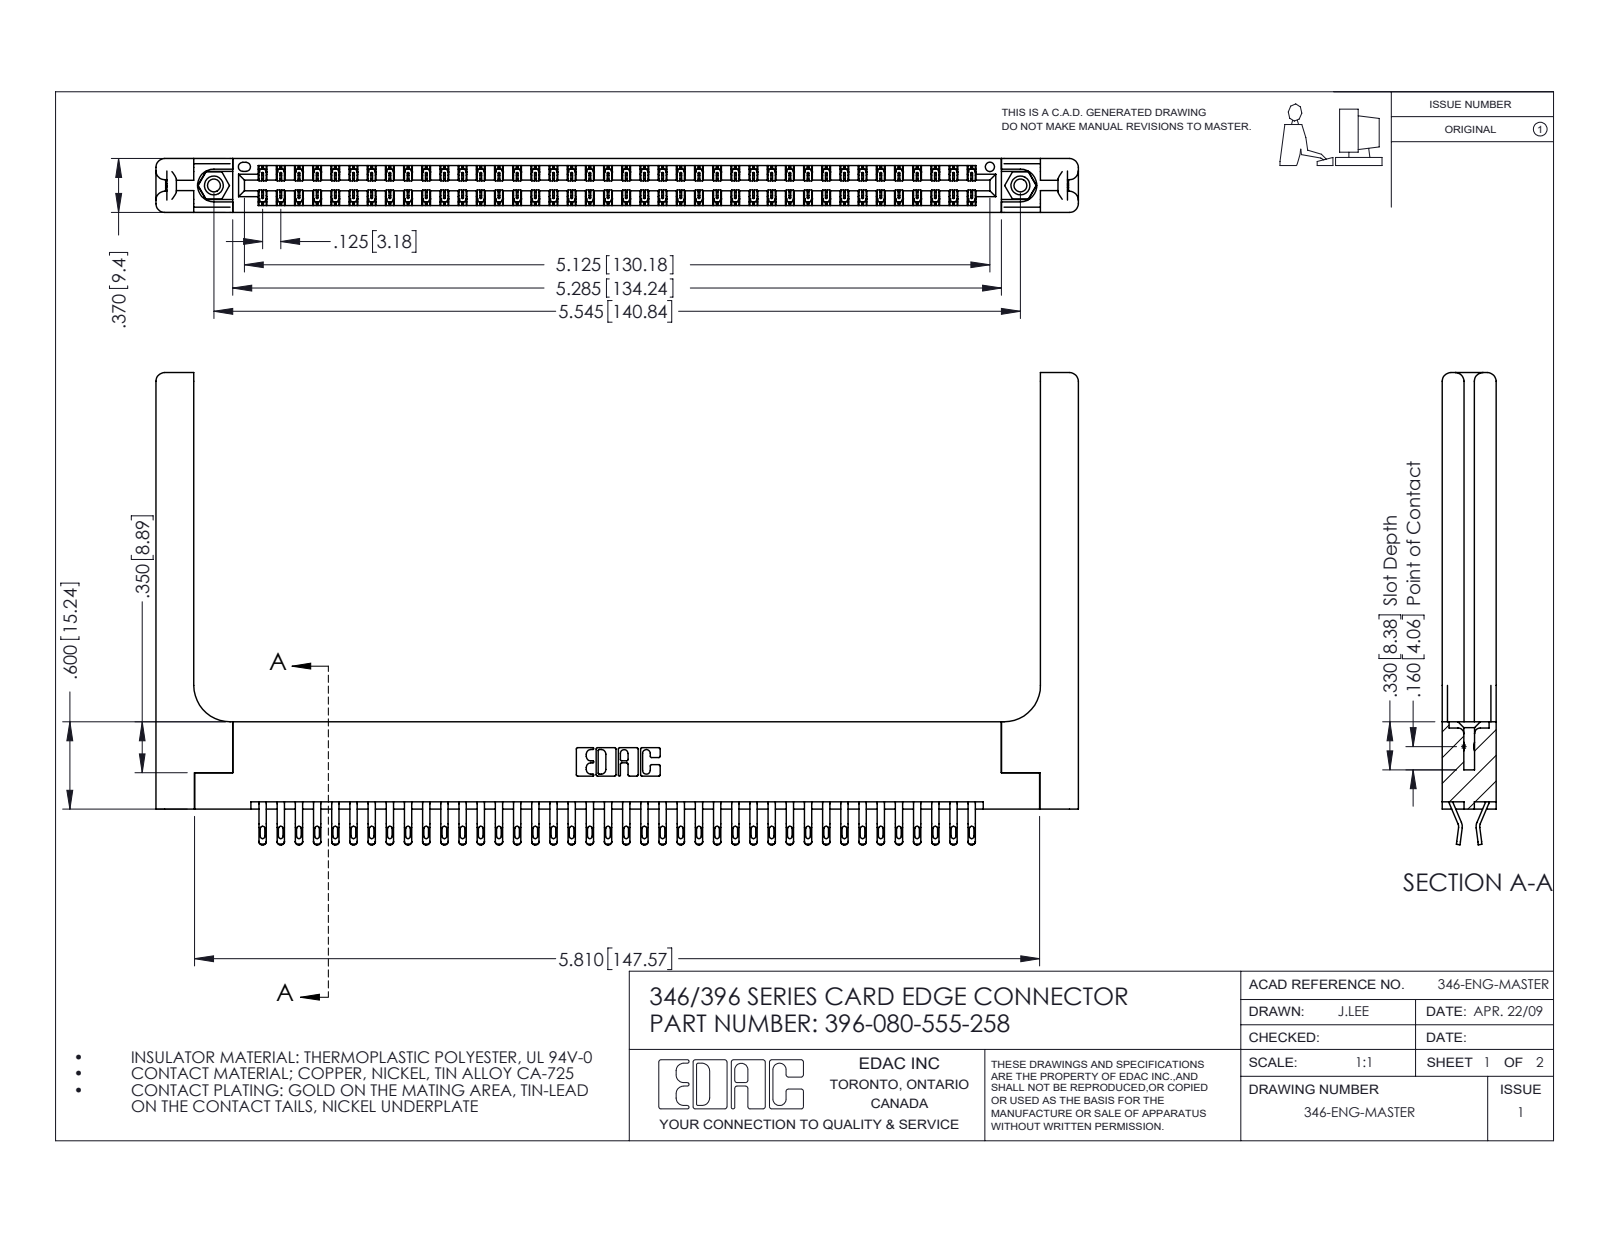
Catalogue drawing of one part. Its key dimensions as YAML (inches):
part_name: "345-250-001_345-250-001-102; 346-220-058_345-220-058; 346 Part_Flush Mounting Lugs - 0.156 Dia-TH; 345-292-001_555 Tail (+1 more)"
step_written_by: "SolidWorks 2016 (CONFIG_CONTROL_DESIGN)"
units: inches
bodies: {solids: 85, faces: 5018, planar: 2864, cylindrical: 2094, other: 60}
overall_size: [6.341, 3.245, 0.37]
volume: 1.429
surface_area: 42.86
round_holes:
  - {diameter: 0.089, count: 2}
  - {diameter: 0.125, count: 2}
  - {diameter: 0.156, count: 2}
  - {diameter: 0.064, count: 1}
round_bosses_or_shafts:
  - {diameter: 0.155, count: 2}
partial_cylinders:
  - {radius: 0.016, count: 160}
  - {radius: 0.02, count: 160}
  - {radius: 0.006, count: 120}
  - {radius: 0.01, count: 22}
  - {radius: 0.06, count: 16}
  - {radius: 0.007, count: 6}
  - {radius: 0.031, count: 6}
  - {radius: 0.026, count: 3}
face_to_face_distances: [0.37, 0.048, 0.322, 0.072, 0.15, 0.148, 0.25, 0.025, 0.298, 0.275]
hole_center_spacings: [0.246, 5.336, 5.545]
